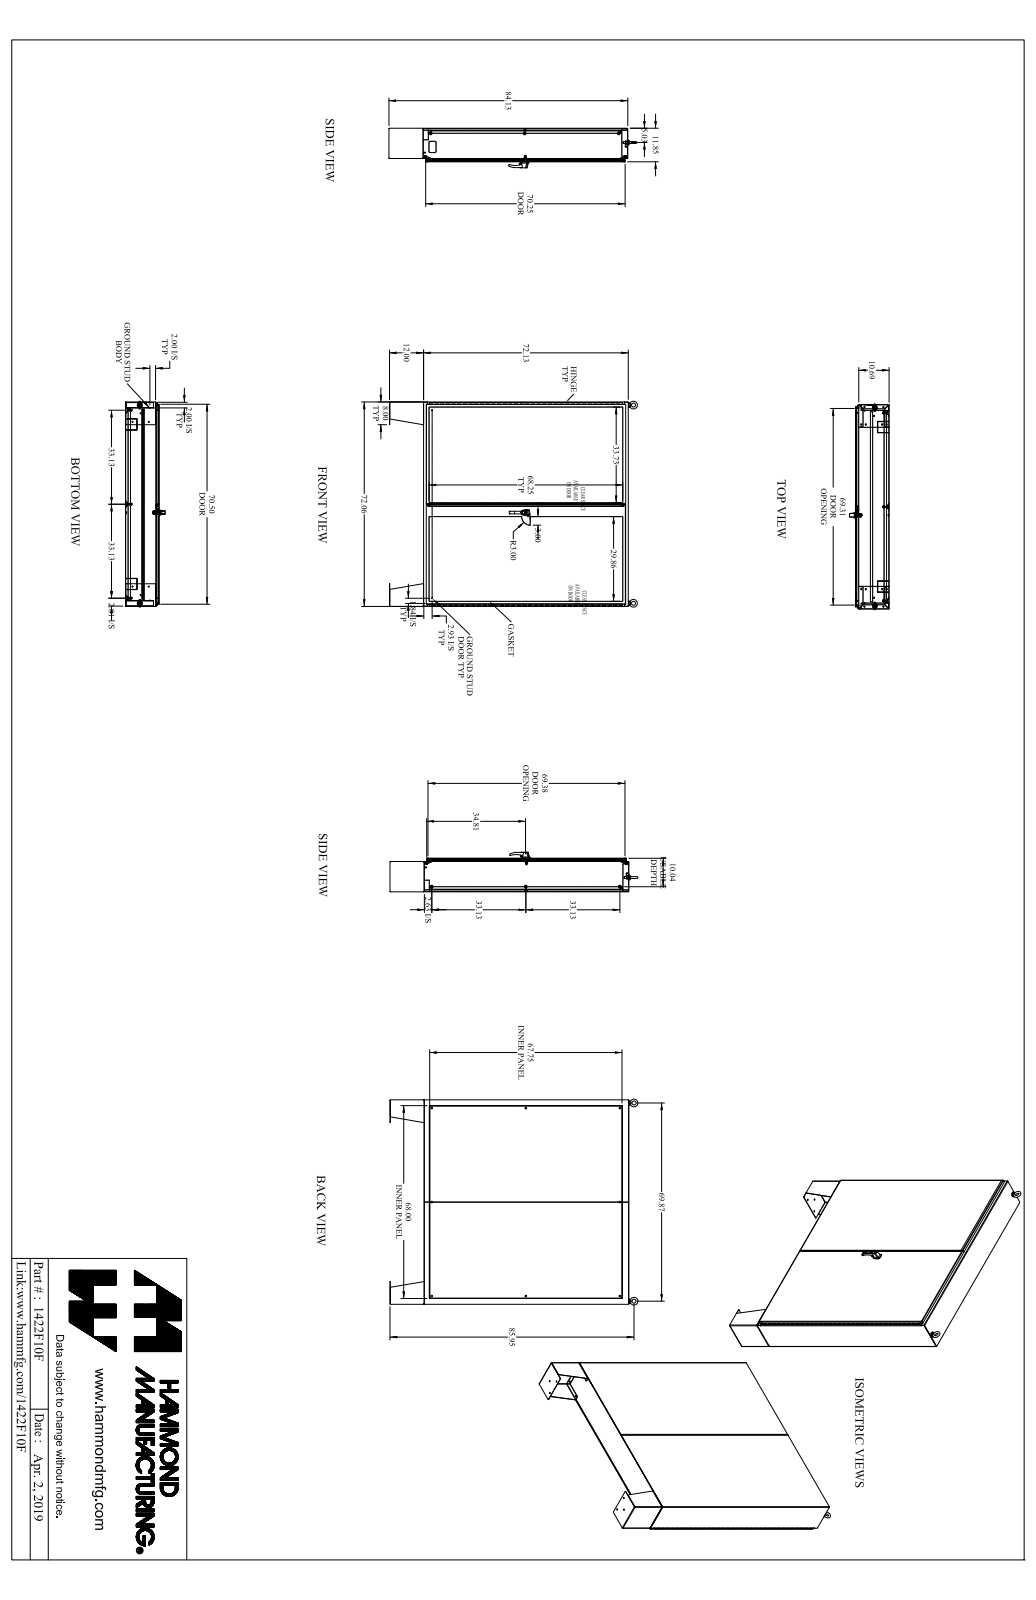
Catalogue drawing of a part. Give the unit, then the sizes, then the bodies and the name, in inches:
Units: inches
Overall size (bounding box): 87.544 × 73.121 × 14.011
Round holes (diameter × count): ⌀0.304 ×34, ⌀0.437 ×14, ⌀0.563 ×8, ⌀0.187 ×2, ⌀0.257 ×2, ⌀0.281 ×2, ⌀0.39 ×2, ⌀0.75 ×2, ⌀0.233 ×1, ⌀0.334 ×1, ⌀0.35 ×1, ⌀0.375 ×1
Round bosses / shafts (diameter × count): ⌀0.65 ×8, ⌀0.375 ×8, ⌀0.33 ×8, ⌀0.386 ×4, ⌀0.218 ×4, ⌀1.25 ×2, ⌀0.738 ×2, ⌀0.37 ×2
Partial cylindrical surfaces — rounded edges, fillets, slot ends (radius × count): R0.048 ×38, R0.143 ×38, R0.06 ×13, R0.116 ×12, R0.188 ×12, R0.185 ×8, R0.03 ×6, R0.09 ×6
Main face-to-face distances: 0.095, 0.125, 11.801, 11.676, 11.771, 11.896, 0.125, 10.209, 10.114, 1.562
Hole centre spacings: 4, 8, 12, 16, 20, 24, 28, 32
Volume: 2 358 in³ · Surface area: 43 328 in²
Bodies: 49 solids, 2438 faces (1222 planar, 981 cylindrical, 235 other)
Part name (STEP PRODUCT): 1422F10F_Default
STEP written by: SolidWorks 2019 (CONFIG_CONTROL_DESIGN)
